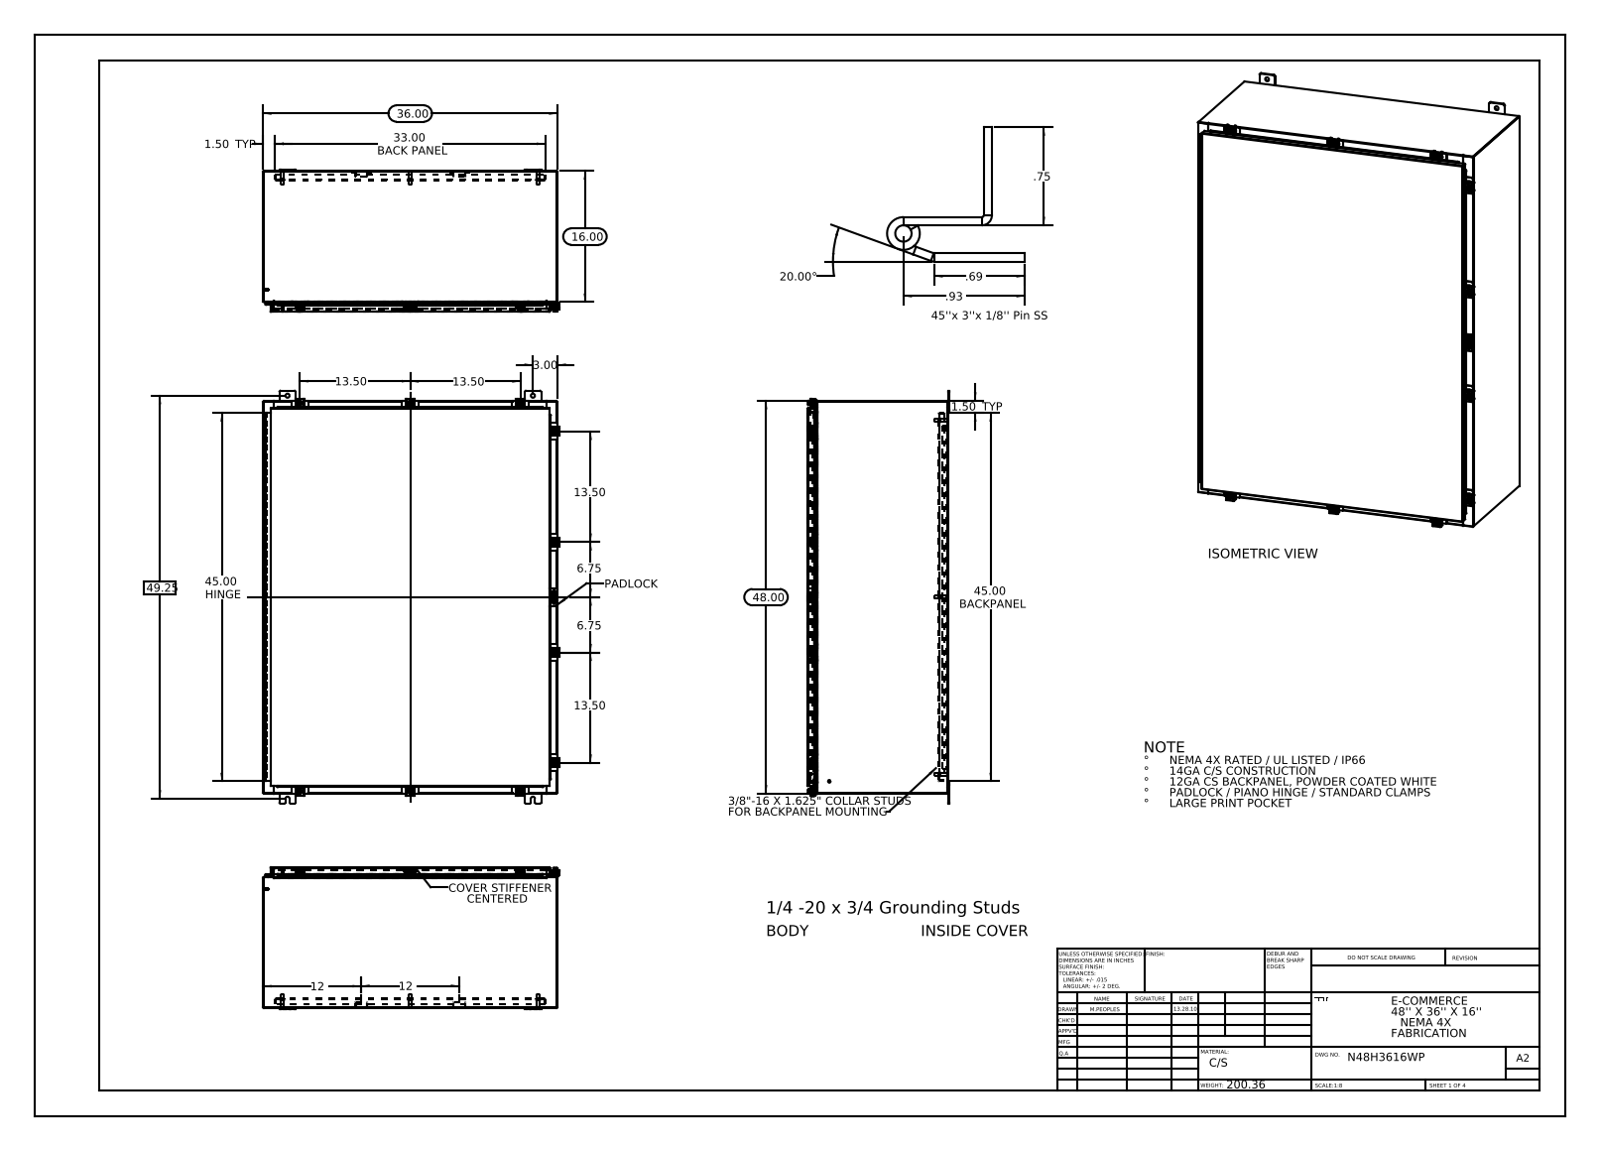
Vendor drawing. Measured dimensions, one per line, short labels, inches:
name: N48H3616SSWP Top; N48H3616SSWP Door Stiffener; N48H3616SSWP Bottom; Quarter-20 CD Stud (+8 more)
written by: SolidWorks 2013 (CONFIG_CONTROL_DESIGN)
unit: in
bodies: 82 solids, 3115 faces (1586 planar, 1301 cylindrical, 228 other)
size: 50.5 × 36.211 × 17.389
volume: 700.9 in³; area: 17 603 in²
holes: 12× ⌀0.5, 10× ⌀0.213, 10× ⌀0.26, 6× ⌀0.25, 2× ⌀0.125
bosses: 11× ⌀0.25, 10× ⌀0.5, 10× ⌀0.399, 8× ⌀0.625, 8× ⌀0.375, 8× ⌀0.33, 6× ⌀0.157, 6× ⌀0.14
rounds: 46× R0.06, 39× R0.013, 33× R0.088, 24× R0.19, 20× R0.12, 20× R0.141, 15× R0.05, 14× R0.08
face distances: 0.075, 17.126, 17.051, 0.104, 17.201, 35.925, 1, 16.126, 1.075, 16.051
hole spacings: 13.5, 13.663, 20, 20.123, 21.625, 23.82, 27, 38.003
